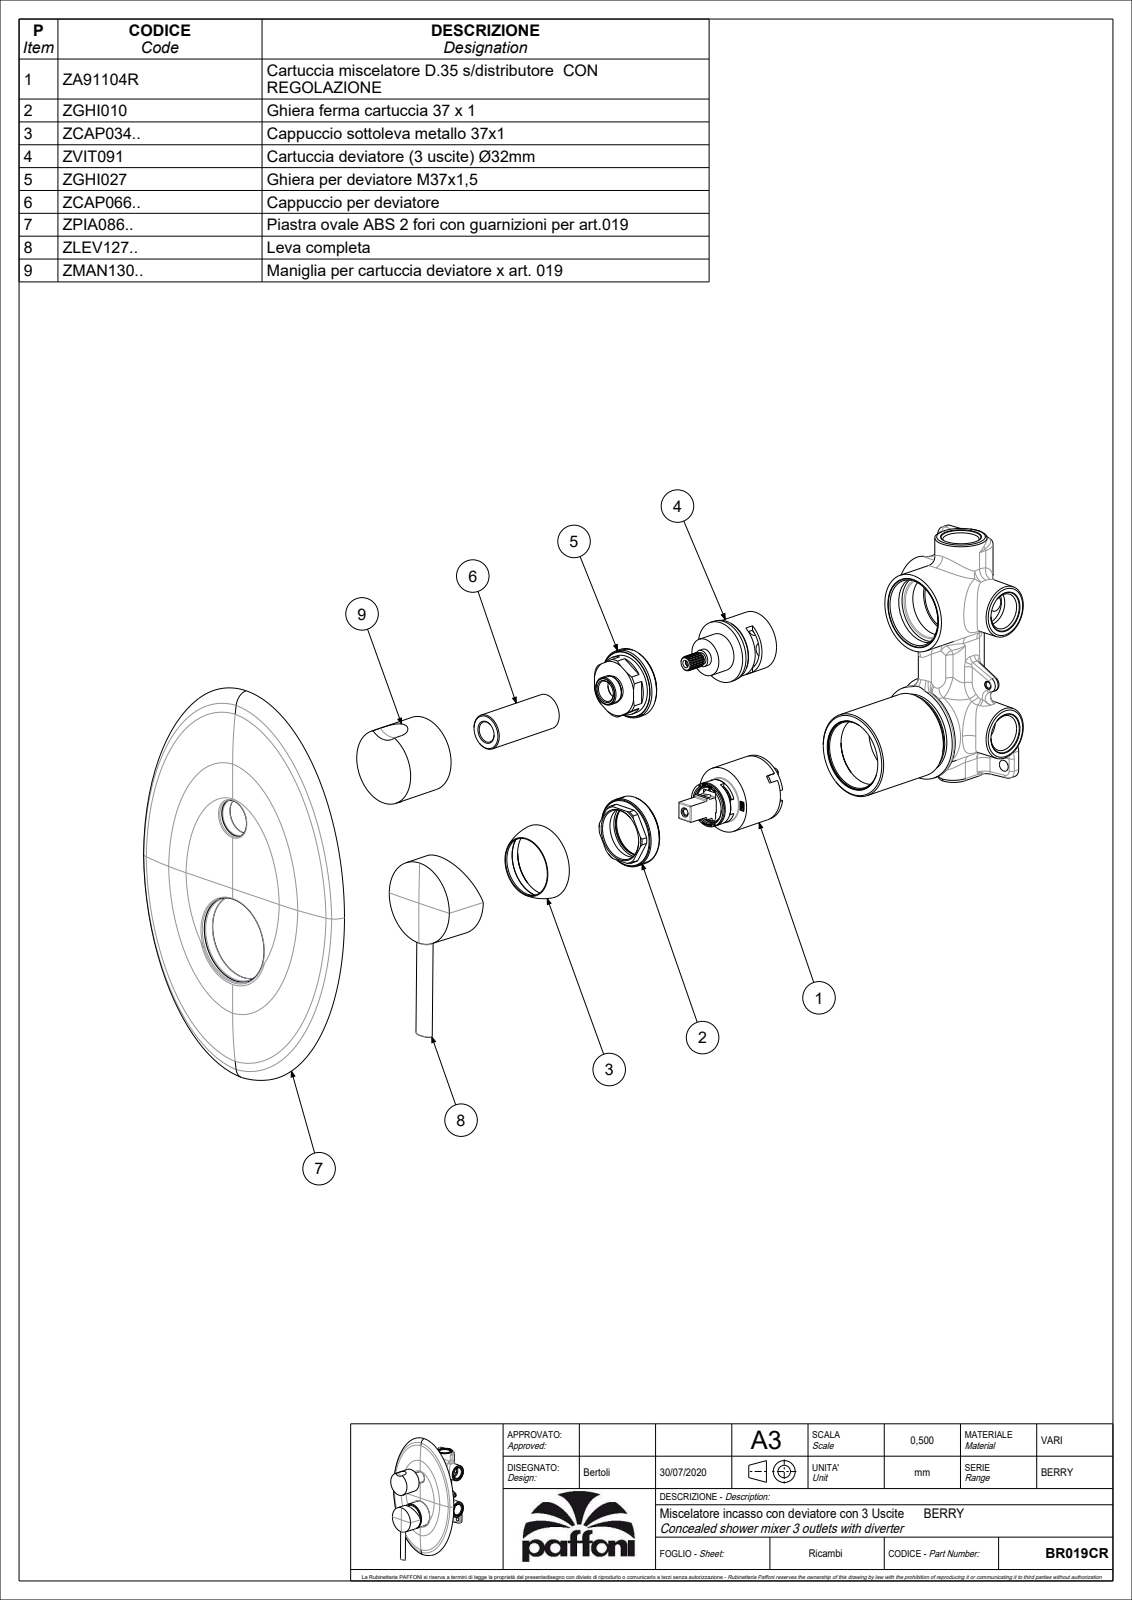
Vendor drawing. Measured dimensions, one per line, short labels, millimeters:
name: BR019CR
written by: CREO PARAMETRIC BY PTC INC, 2020044 (CONFIG_CONTROL_DESIGN)
unit: mm
bodies: 4 solids, 1287 faces (718 planar, 312 cylindrical, 257 other)
size: 216 × 146 × 63.25
volume: 142 139 mm³; area: 107 868 mm²
holes: 2× ⌀3, 2× ⌀4, 2× ⌀12.7, 2× ⌀36, 1× ⌀3.2, 1× ⌀3.3, 1× ⌀3.5, 1× ⌀4.2, 1× ⌀4.5, 1× ⌀5, 1× ⌀8, 1× ⌀11
bosses: 2× ⌀9.3, 1× ⌀51, 1× ⌀49, 1× ⌀44.8, 1× ⌀40, 1× ⌀35, 1× ⌀34.8, 1× ⌀32.2
rounds: 27× R0.5, 11× R0.15, 8× R0.3, 4× R1, 4× R1.25, 2× R0.8, 2× R2.75, 1× R2.5
face distances: 54.5, 9, 3.8, 7.6, 50.7, 24.5, 30, 1.8, 34.1, 46.9
hole spacings: 8.6, 73.33, 83.29, 6.9, 7.9, 10, 14, 14.8
